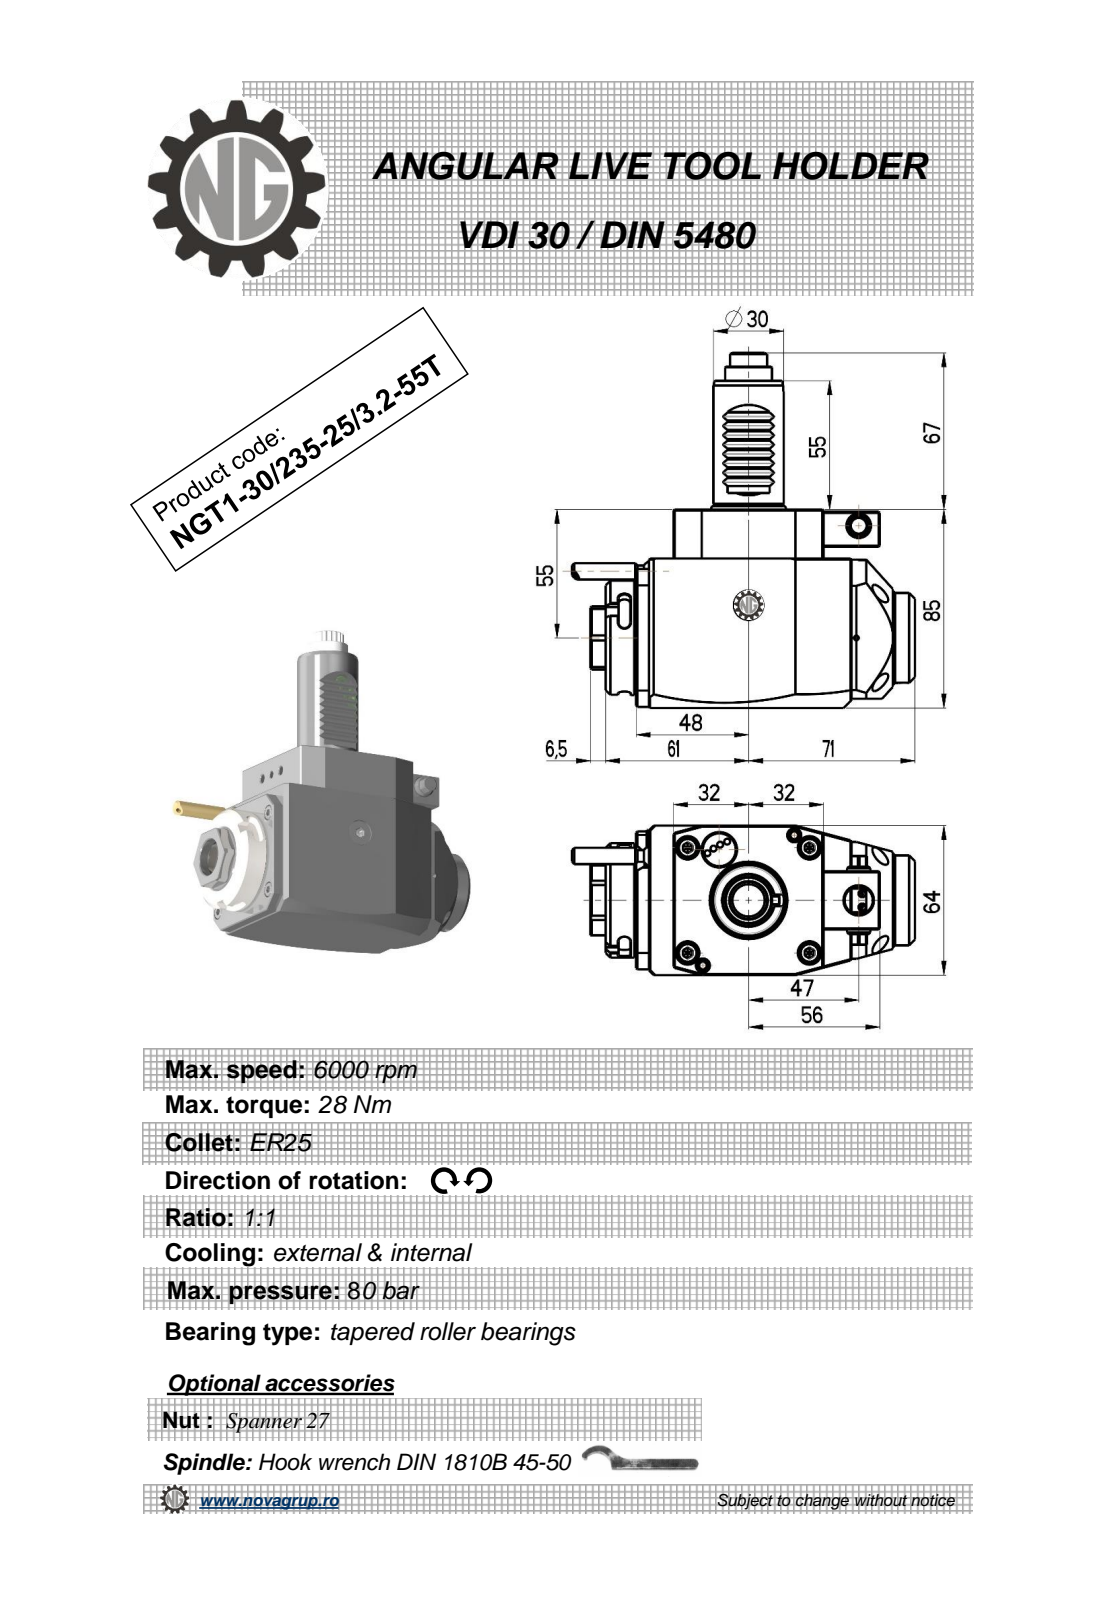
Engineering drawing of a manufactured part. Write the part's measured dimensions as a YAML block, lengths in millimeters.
part_name: "NGT1_30_235_25_3_2_55T"
step_written_by: "PRO/ENGINEER BY PARAMETRIC TECHNOLOGY CORPORATION, 2010280 (CONFIG_CONTROL_DESIGN)"
units: millimeters
bodies: {solids: 1, faces: 433, planar: 188, cylindrical: 155, other: 90}
overall_size: [152, 146.38, 64]
volume: 569947
surface_area: 51891
round_holes:
  - {diameter: 2.5, count: 1}
  - {diameter: 3, count: 1}
  - {diameter: 9.5, count: 1}
  - {diameter: 12, count: 1}
  - {diameter: 18, count: 1}
round_bosses_or_shafts:
  - {diameter: 8, count: 2}
  - {diameter: 49, count: 1}
  - {diameter: 42, count: 1}
  - {diameter: 38.5, count: 1}
  - {diameter: 30, count: 1}
  - {diameter: 20, count: 1}
  - {diameter: 10, count: 1}
  - {diameter: 7, count: 1}
partial_cylinders:
  - {radius: 1.98, count: 36}
  - {radius: 0.3, count: 8}
  - {radius: 2.5, count: 6}
  - {radius: 180, count: 2}
  - {radius: 3.85, count: 1}
  - {radius: 4.25, count: 1}
  - {radius: 4.5, count: 1}
  - {radius: 7.08, count: 1}
face_to_face_distances: [64, 85, 16, 13, 21, 80, 29, 119, 132, 103]
hole_center_spacings: [26.17, 34.25, 46.5]
